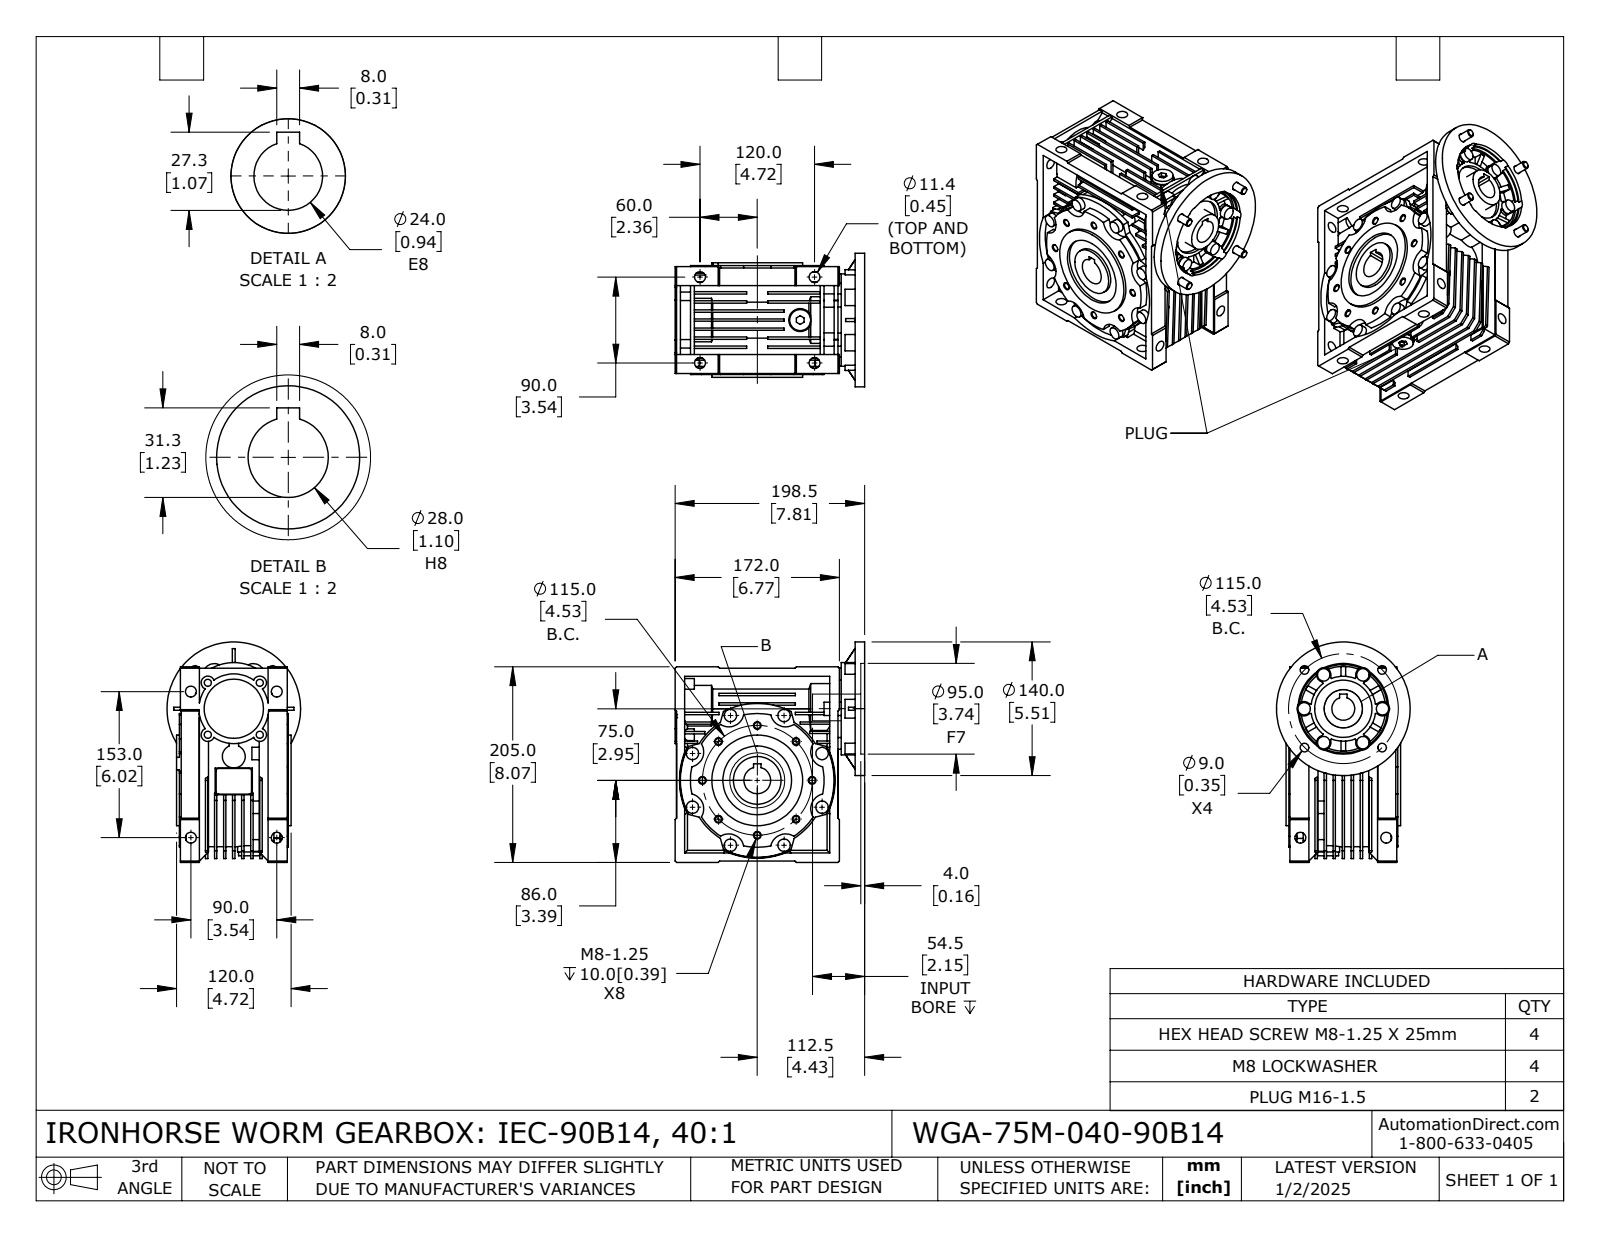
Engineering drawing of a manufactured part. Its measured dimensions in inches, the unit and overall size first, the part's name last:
Units: inches
Overall size (bounding box): 9.094 × 8.327 × 5.512
Round holes (diameter × count): ⌀0.262 ×8, ⌀0.448 ×8, ⌀0.293 ×4, ⌀0.323 ×4, ⌀0.354 ×4, ⌀0.571 ×2, ⌀0.945 ×1, ⌀0.984 ×1, ⌀1.102 ×1, ⌀1.535 ×1, ⌀1.654 ×1, ⌀1.969 ×1
Round bosses / shafts (diameter × count): ⌀0.512 ×14, ⌀0.606 ×4, ⌀0.315 ×4, ⌀0.945 ×3, ⌀0.866 ×2, ⌀0.622 ×2, ⌀0.539 ×2, ⌀5.512 ×1
Partial cylindrical surfaces — rounded edges, fillets, slot ends (radius × count): R0.276 ×10, R0.63 ×8, R0.295 ×6, R0.463 ×6, R0.098 ×4, R1.417 ×1, R1.437 ×1, R1.535 ×1
Main face-to-face distances: 0.374, 0.098, 0.748, 0.472, 0.394, 0.276, 1.122, 0.65, 1.093, 0.846
Hole centre spacings: 2.264, 3.202, 1.733, 2.724, 4.183, 4.528, 0.748, 1.515
Volume: 176.2 in³ · Surface area: 769.9 in²
Bodies: 16 solids, 1349 faces (749 planar, 444 cylindrical, 156 other)
Part name (STEP PRODUCT): WGA-75M-040-90B14
STEP written by: SolidWorks 2024 (CONFIG_CONTROL_DESIGN)
